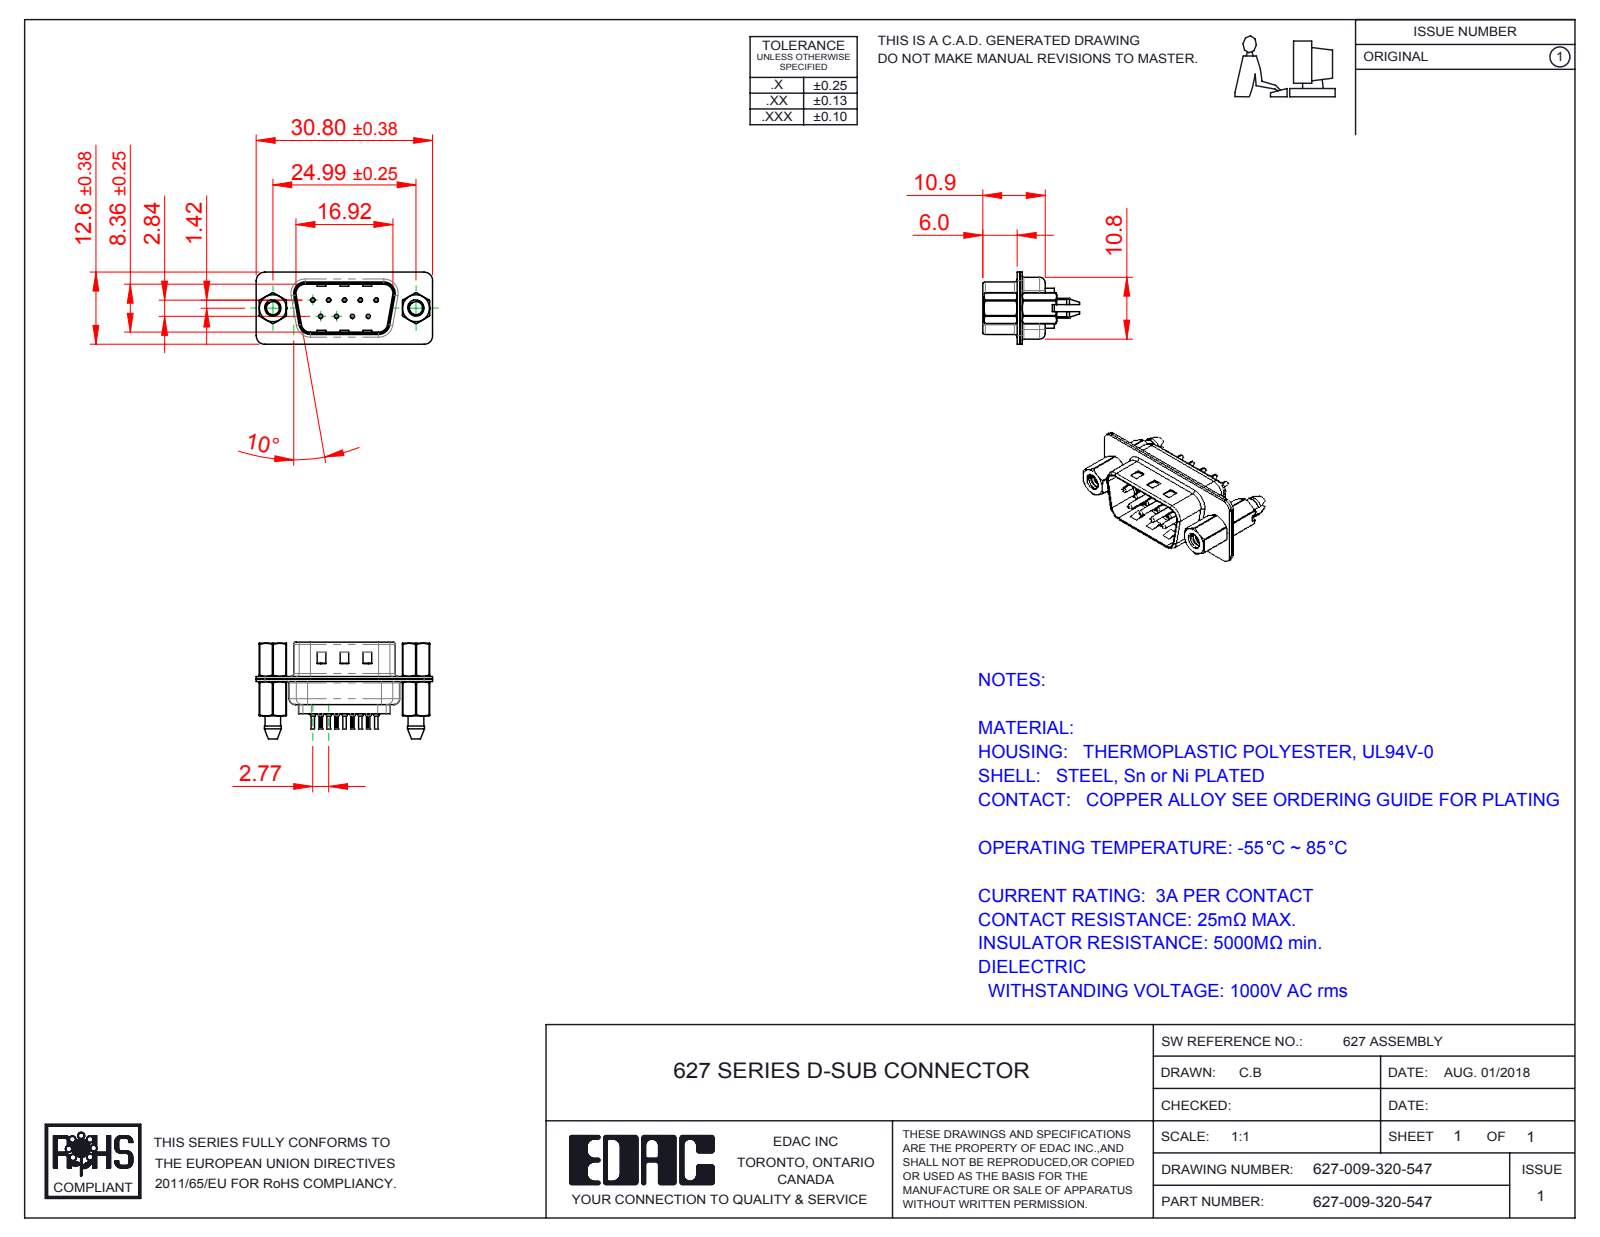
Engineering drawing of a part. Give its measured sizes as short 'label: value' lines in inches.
name: 627 Contact Row 1_20L; 627 Housing_09 LP; 627 Shell Front_09 Contacts; 627 Shell Rear_09 Contacts (+4 more)
written by: SolidWorks 2016 (CONFIG_CONTROL_DESIGN)
unit: in
bodies: 16 solids, 1386 faces (377 planar, 566 cylindrical, 443 other)
size: 1.213 × 0.665 × 0.496
volume: 0.1 in³; area: 7.214 in²
holes: 9× ⌀0.008, 9× ⌀0.014, 9× ⌀0.043, 9× ⌀0.063, 2× ⌀0.089, 2× ⌀0.09, 2× ⌀0.157, 2× ⌀0.189
bosses: 9× ⌀0.079, 9× ⌀0.059, 9× ⌀0.03, 9× ⌀0.024, 2× ⌀0.193, 2× ⌀0.11
rounds: 20× R0.059, 18× R0.004, 12× R0.079, 10× R0.063, 8× R0.02, 4× R0.01, 4× R0.024, 4× R0.026
face distances: 0.018, 0.016, 0.035, 0.032, 0.377, 0.055, 0.187, 0.345, 0.256, 0.02
hole spacings: 0.124, 0.109, 0.218, 0.198, 0.198, 0.327, 0.294, 0.295
